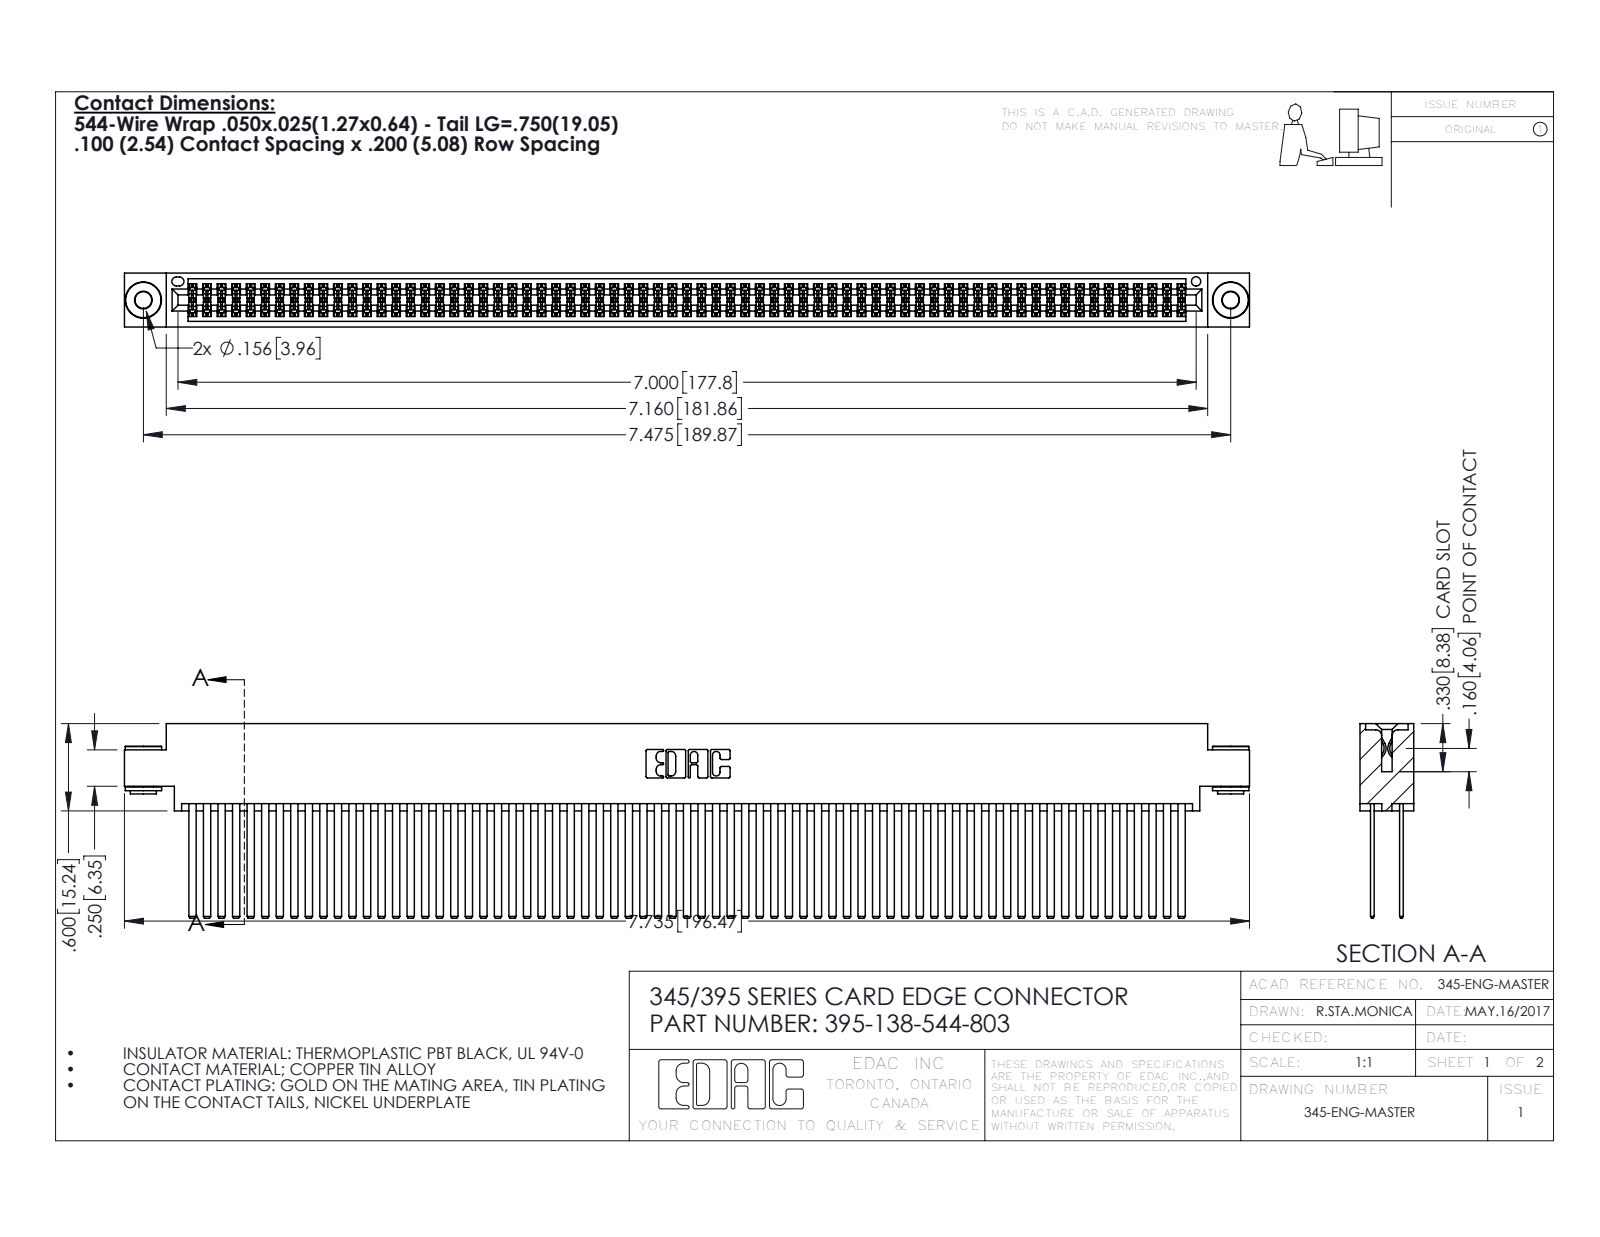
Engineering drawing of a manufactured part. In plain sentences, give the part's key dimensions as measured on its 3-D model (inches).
The part is named "345-250-002_345-250-002-102; 395-138-544-803; 345-292-001_345-293-144; 345 Part_0.170 Offset - 0.156 Dia-TH". Its 3-D file was written by "SolidWorks 2016 (CONFIG_CONTROL_DESIGN)". It is 141 solids with 6240 faces: 4096 planar, 2136 cylindrical and 8 other. Overall it measures 7.735 by 1.337 by 0.37 inches. Its volume is 1.292 cubic inches and its surface area 58.66 square inches. Round holes: 2 of diameter 0.116, 2 of diameter 0.156, 1 of diameter 0.064. Round bosses or shafts: 2 of diameter 0.25, 2 of diameter 0.18, 2 of diameter 0.136. Partial cylindrical surfaces (rounded edges, fillets, slot ends): 207 of radius 0.006, 22 of radius 0.01, 6 of radius 0.007, 6 of radius 0.031, 3 of radius 0.026, 2 of radius 0.014, 2 of radius 0.019, 2 of radius 0.022. The main face-to-face distances are 0.2, 0.025, 0.072, 0.098, 0.272, 0.298, 0.225, 0.175, 0.37, 0.15. The hole center spacings are 0.27, 7.239, 7.475.
